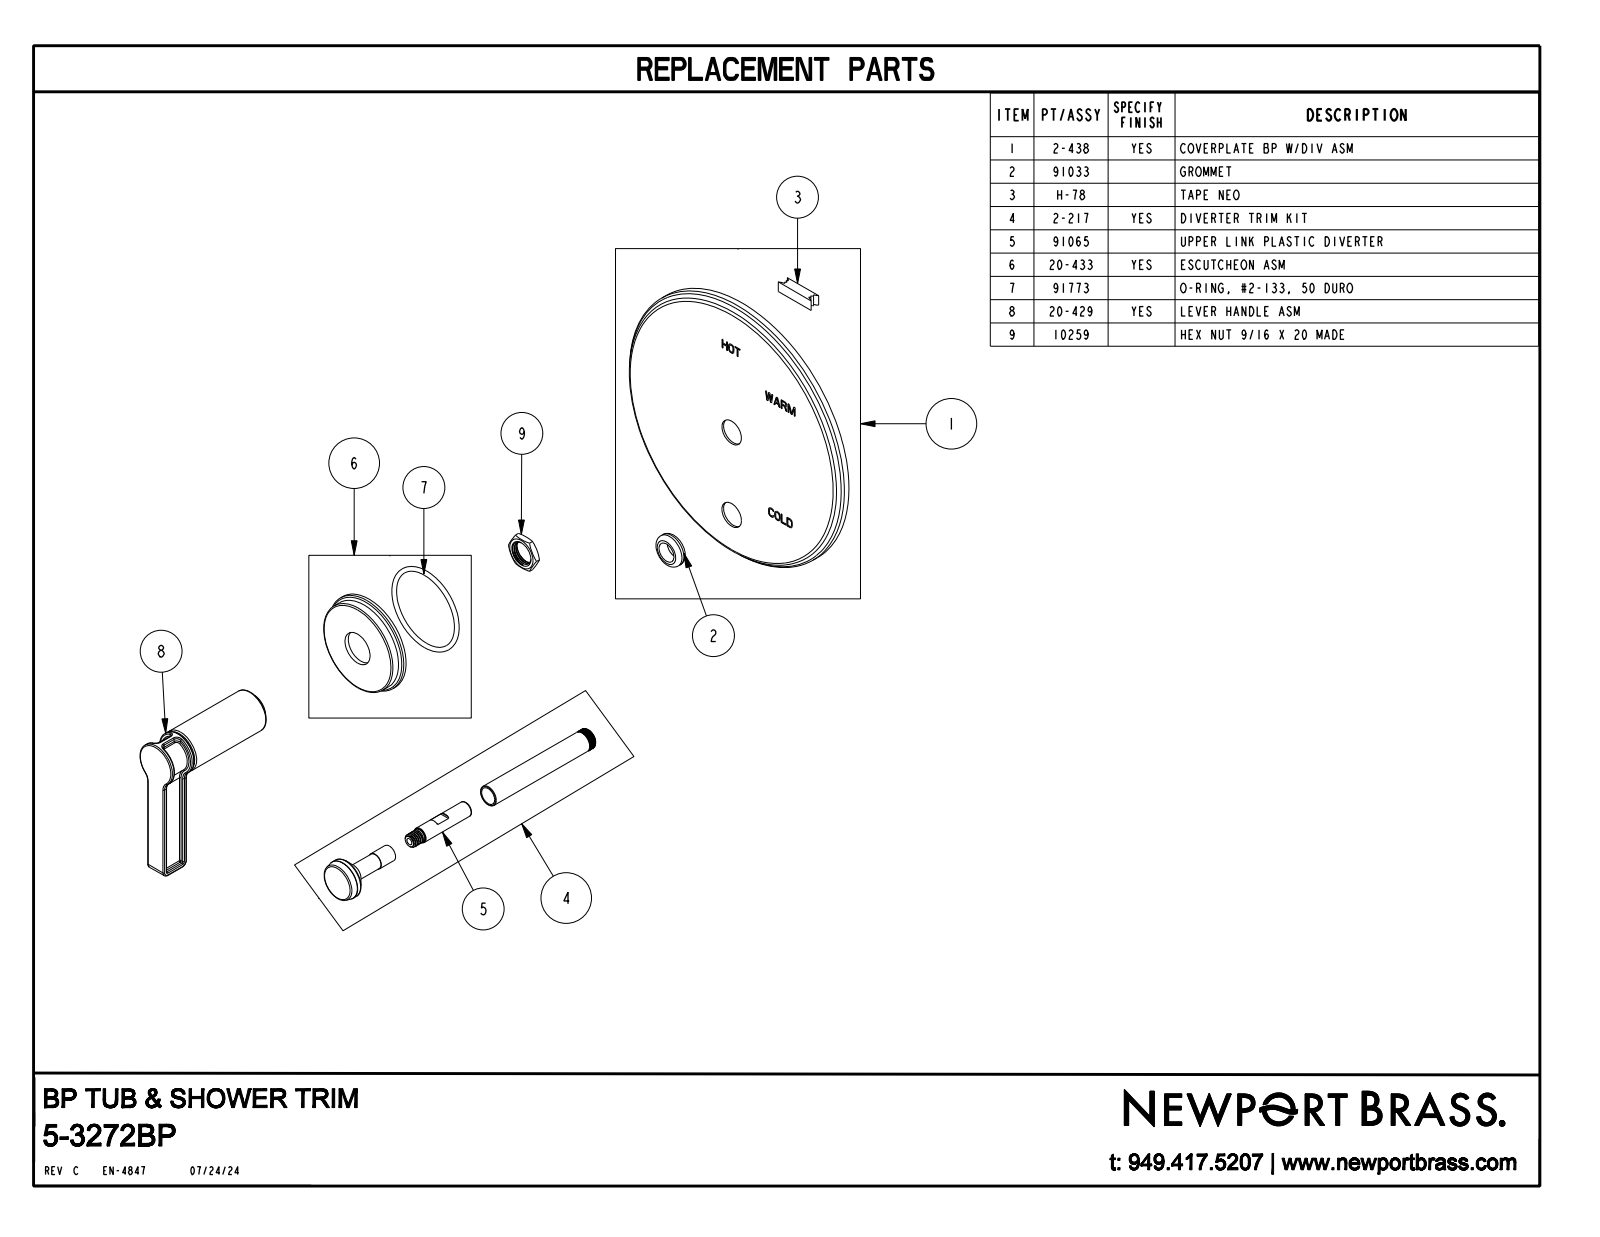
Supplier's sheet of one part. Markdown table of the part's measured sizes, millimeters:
| quantity | value |
| --- | --- |
| part name | 11118_AF2; 91033; H-78; 2-438_AF2_ASM (+8 more) |
| STEP written by | CREO PARAMETRIC BY PTC INC, 2018400 (CONFIG_CONTROL_DESIGN) |
| units | millimeters |
| bodies | 17 solids, 1229 faces (474 planar, 440 cylindrical, 315 other) |
| overall size | 165.1 × 165.1 × 155 |
| volume | 85 850 mm³ |
| surface area | 126 500 mm² |
| round holes (diameter × count) | 2.8 × 1, 3.8 × 1, 4.3 × 1, 6.7 × 1, 7 × 1, 8.1 × 1, 8.8 × 1, 9.1 × 1, 9.1 × 1, 9.5 × 1, 9.7 × 1, 10.1 × 1 |
| round bosses / shafts (diameter × count) | 165.1 × 1, 57.2 × 1, 53.1 × 1, 46 × 1, 24.8 × 1, 22.9 × 1, 21.6 × 1, 18.5 × 1 |
| partial cylindrical surfaces (radius × count) | 0.6 × 22, 0.3 × 6, 1.1 × 6, 2.5 × 4, 0.8 × 2, 3.3 × 2, 6.4 × 2, 8.9 × 2 |
| main face-to-face distances | 1.3, 10.2, 8.9, 2.5, 73.7, 7.6, 83.8, 82.6, 17.8, 66.1 |
| hole center spacings | 55.1 |
